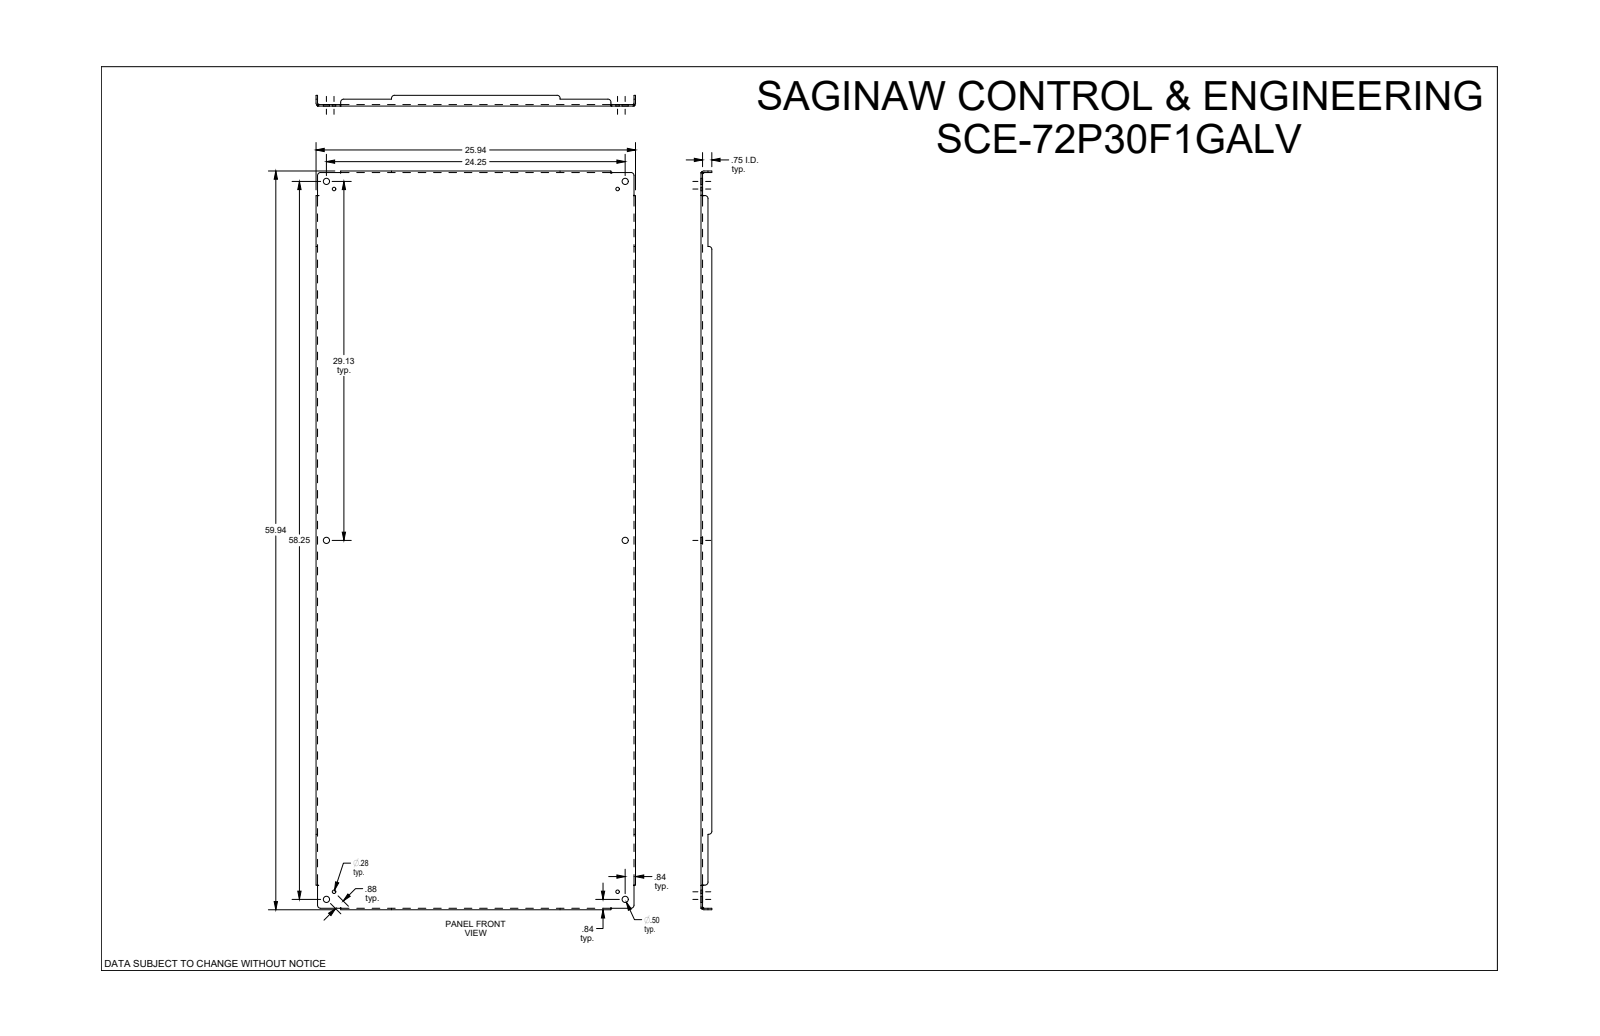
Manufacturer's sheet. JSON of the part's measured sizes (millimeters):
{"part_name": "SCE-72P30F1GALV", "step_written_by": "SolidWorks 2019 (CONFIG_CONTROL_DESIGN)", "units": "millimeters", "bodies": {"solids": 1, "faces": 108, "planar": 46, "cylindrical": 38, "other": 24}, "overall_size": [1522.4, 658.8, 22.2], "volume_mm3": 3371000, "surface_area_mm2": 2139000, "round_holes": [[12.7, 6], [7.1, 4]], "partial_cylinders_radius": [[6.4, 12], [2.8, 4], [6, 4]], "face_to_face_distances": [3.2, 3.2, 655.7, 652.4, 658.8, 1519.3, 19.1, 22.2, 1516, 1522.4], "hole_center_spacings": [22.2, 600.4, 724.2, 739.8, 940.5, 962.6, 1463.9, 1582.1]}
